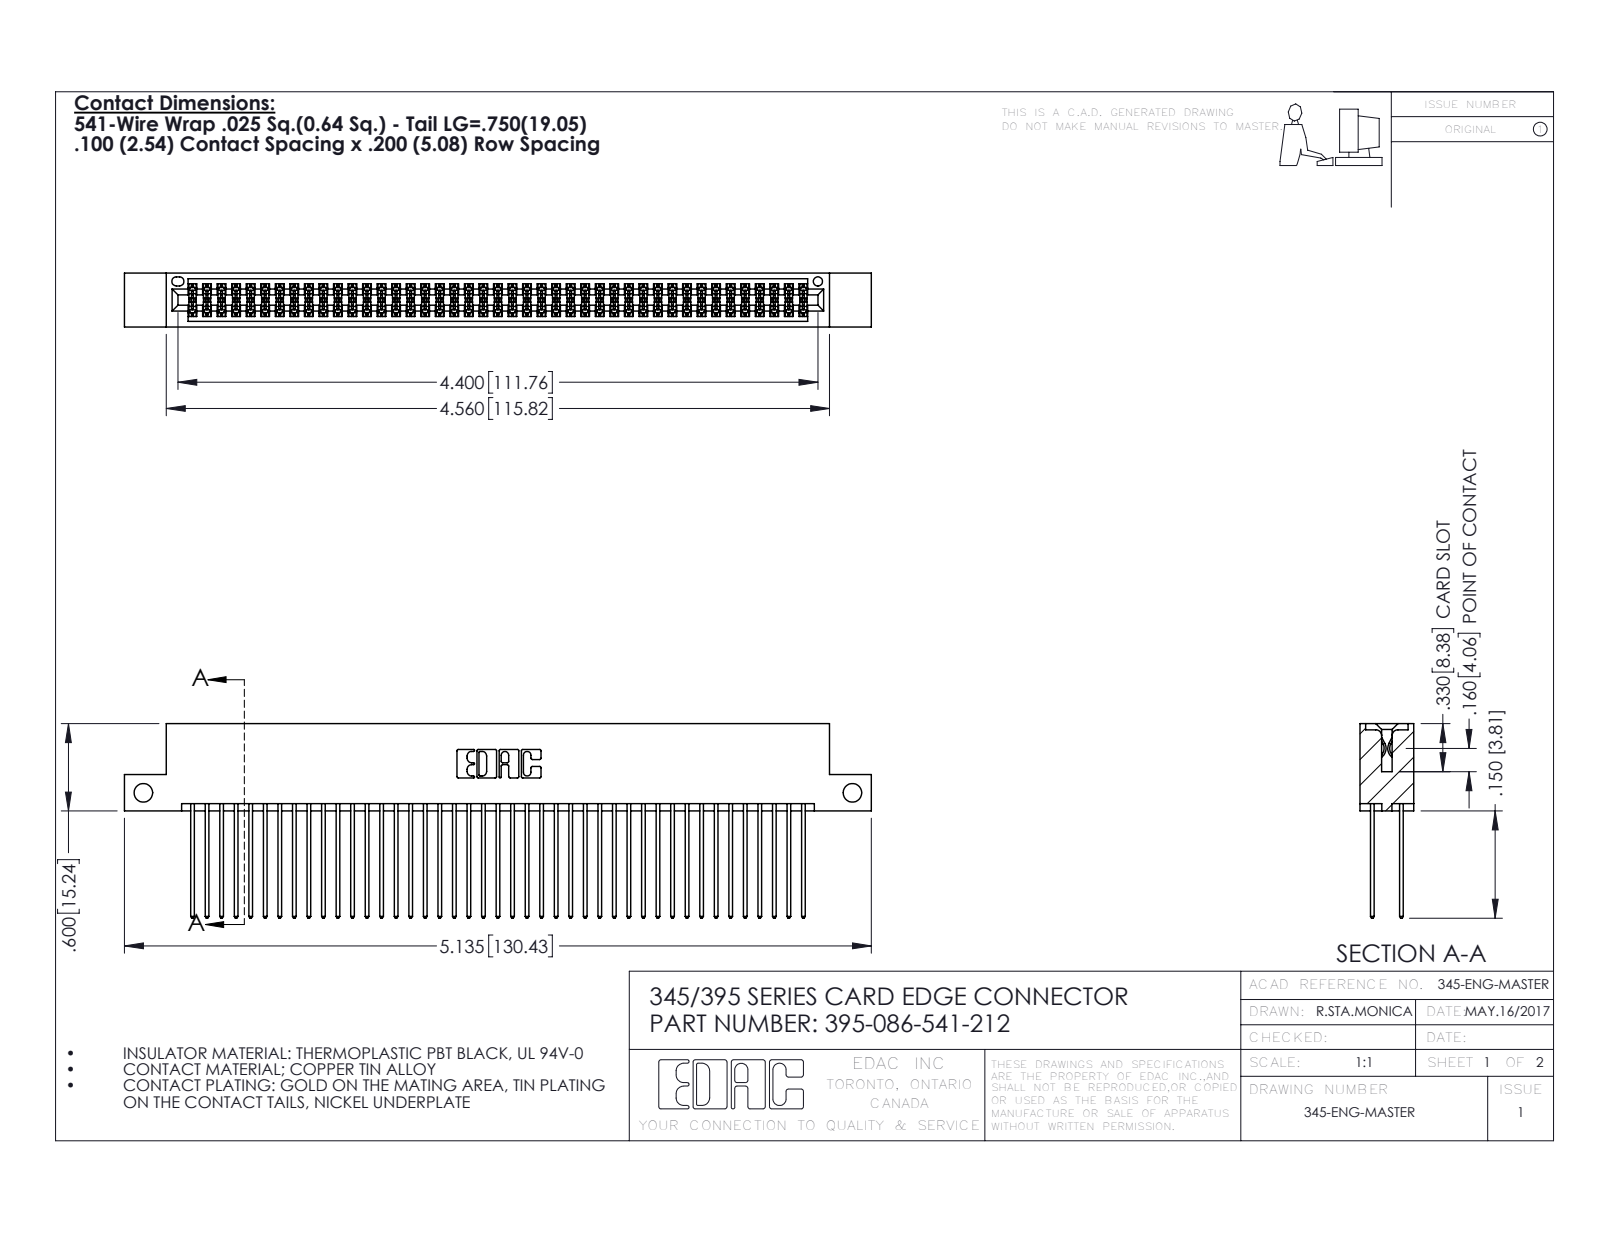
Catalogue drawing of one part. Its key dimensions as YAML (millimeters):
part_name: "345-292-001_345-293-141; 395-086-541-212; 345 Part_Flush Mounting Lugs - Side Mount"
step_written_by: "SolidWorks 2016 (CONFIG_CONTROL_DESIGN)"
units: millimeters
bodies: {solids: 87, faces: 4426, planar: 2918, cylindrical: 1508, other: 0}
overall_size: [130.4, 34, 9.4]
volume: 13100
surface_area: 21550
round_holes:
  - {diameter: 3.3, count: 2}
  - {diameter: 1.6, count: 1}
partial_cylinders:
  - {radius: 0.2, count: 129}
  - {radius: 0.3, count: 86}
  - {radius: 0.3, count: 22}
  - {radius: 0.2, count: 6}
  - {radius: 0.8, count: 6}
  - {radius: 0.7, count: 3}
  - {radius: 0.4, count: 2}
  - {radius: 0.5, count: 2}
face_to_face_distances: [7.6, 1.8, 5.1, 2.5, 6.9, 0.6, 5.7, 9.4, 4.4, 3.8]
hole_center_spacings: [123.8]
